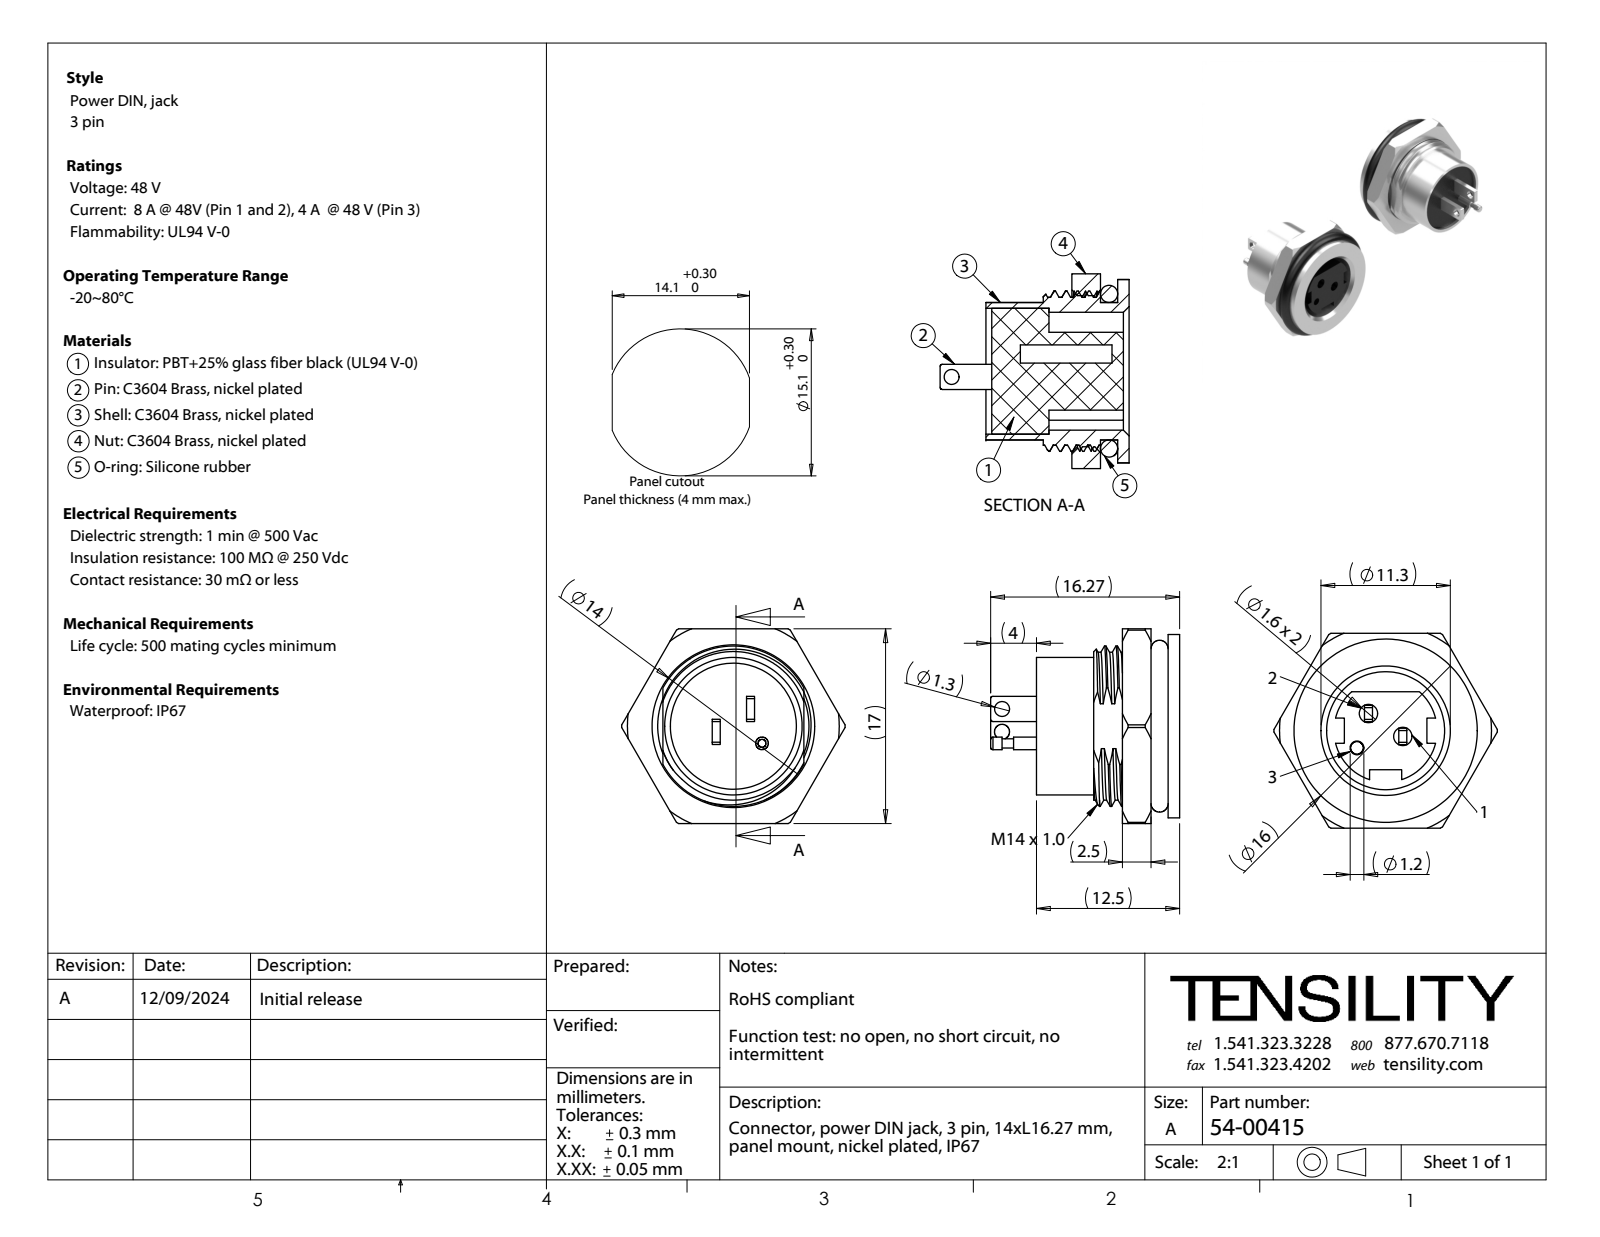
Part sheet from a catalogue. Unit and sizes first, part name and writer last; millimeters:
Units: millimetres
Overall size (bounding box): 19.5 × 17 × 16.5
Round holes (diameter × count): ⌀1.3 ×2, ⌀1.6 ×2, ⌀3 ×2, ⌀1.1 ×1, ⌀1.2 ×1, ⌀1.8 ×1, ⌀10.3 ×1, ⌀11 ×1, ⌀13.2 ×1
Round bosses / shafts (diameter × count): ⌀16 ×1, ⌀12 ×1, ⌀0.8 ×1
Partial cylindrical surfaces — rounded edges, fillets, slot ends (radius × count): R0.2 ×8, R0.3 ×4, R0.8 ×2, R4.5 ×1, R7 ×1, R9.75 ×1
Main face-to-face distances: 5, 2.5, 7, 0.5, 4.5, 2, 1, 1.5, 9.5, 12
Hole centre spacings: 1.58, 2, 2.12, 2.92, 3.16, 3.61, 4.12
Volume: 1 572 mm³ · Surface area: 3 074 mm²
Bodies: 7 solids, 235 faces (89 planar, 80 cylindrical, 66 other)
Part name (STEP PRODUCT): 54-00415-04_默认; 54-00415-05_默认; 54-00415-06_默认; 54-00415-01_默认 (+3 more)
STEP written by: SolidWorks 2025 (CONFIG_CONTROL_DESIGN)
